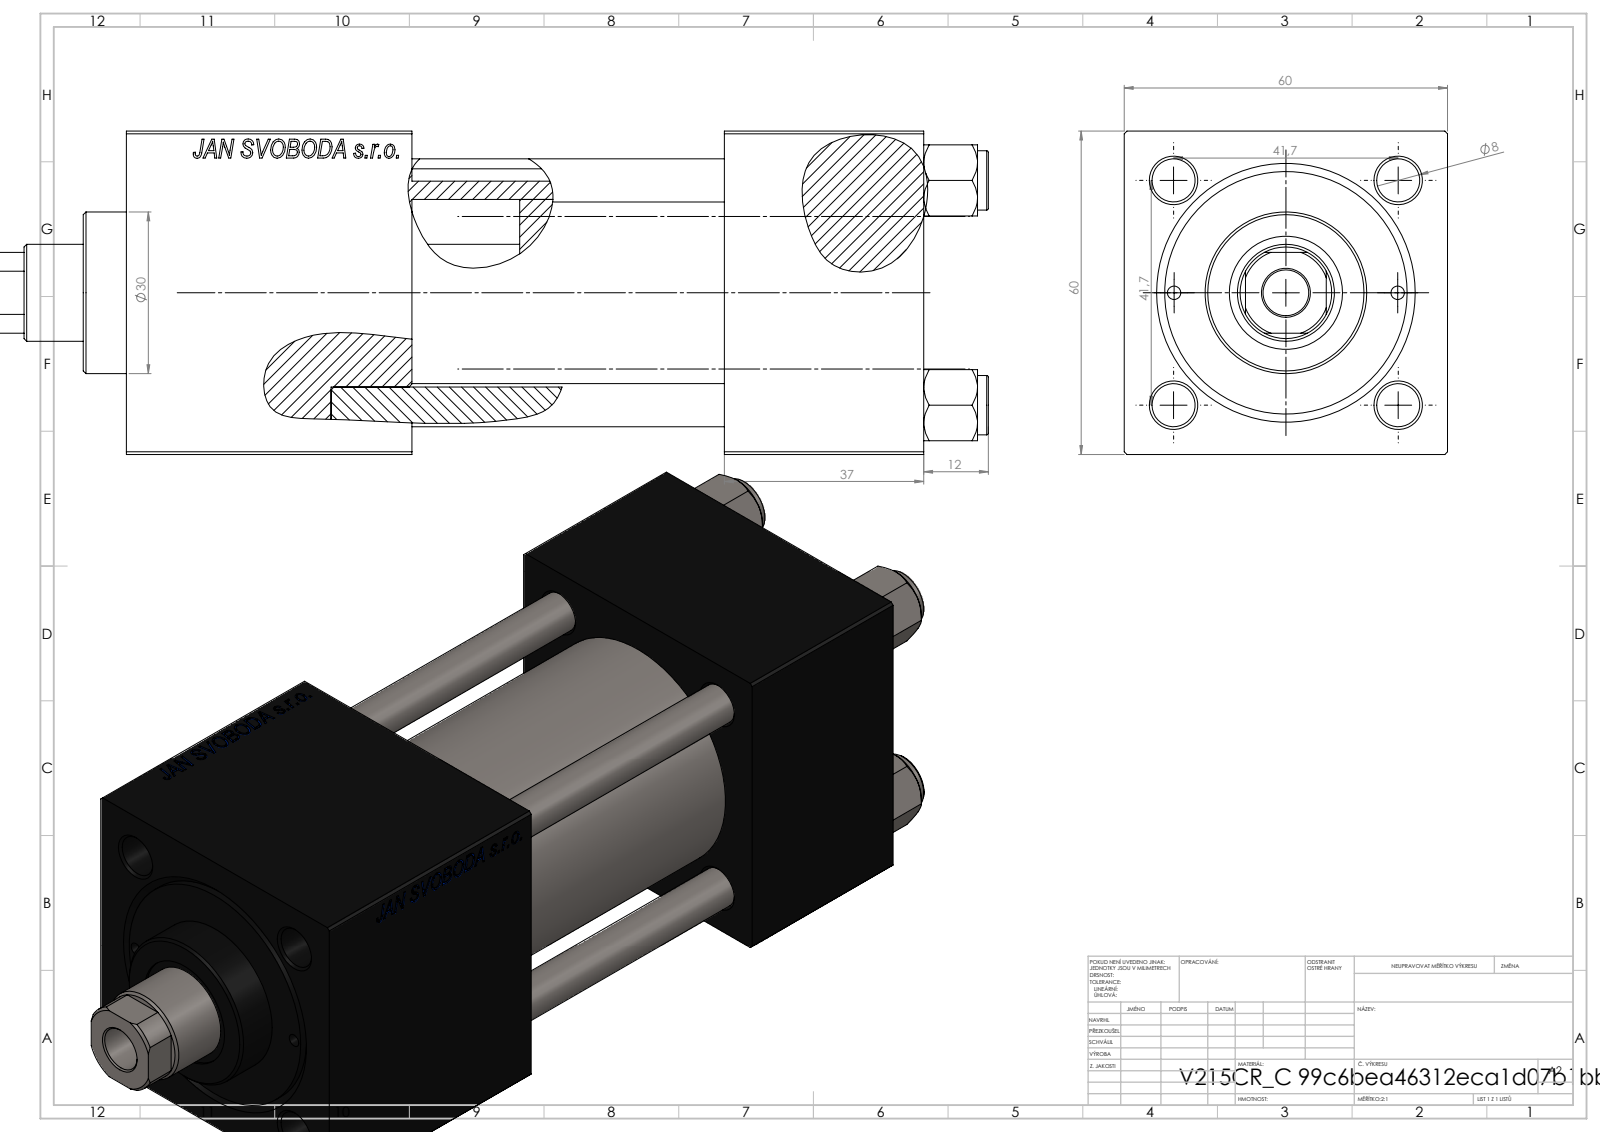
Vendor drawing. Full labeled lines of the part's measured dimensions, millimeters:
Part name (STEP PRODUCT): V215CR_C_Body; V215CR_VCP_C; V215CR_C_TYCINKA; NUT_M5_C (+1 more)
STEP written by: SolidWorks 2019 (CONFIG_CONTROL_DESIGN)
Units: millimetres
Bodies: 11 solids, 1154 faces (528 planar, 90 cylindrical, 536 other)
Overall size (bounding box): 185 × 60 × 60
Volume: 402 520 mm³ · Surface area: 105 408 mm²
Round holes (diameter × count): ⌀8 ×4, ⌀2.5 ×2, ⌀7 ×2, ⌀16.66 ×2, ⌀24 ×2, ⌀8.5 ×1, ⌀18 ×1, ⌀21 ×1, ⌀31 ×1, ⌀40 ×1, ⌀45 ×1
Round bosses / shafts (diameter × count): ⌀11 ×4, ⌀46 ×1, ⌀30 ×1
Partial cylindrical surfaces — rounded edges, fillets, slot ends (radius × count): R8.5 ×1
Main face-to-face distances: 60, 37, 53, 148, 111, 58, 95, 119.3, 82.3, 24.3
Hole centre spacings: 20.85, 29.49, 41.7, 46.53, 20.75, 58.97, 41.5, 92.5
